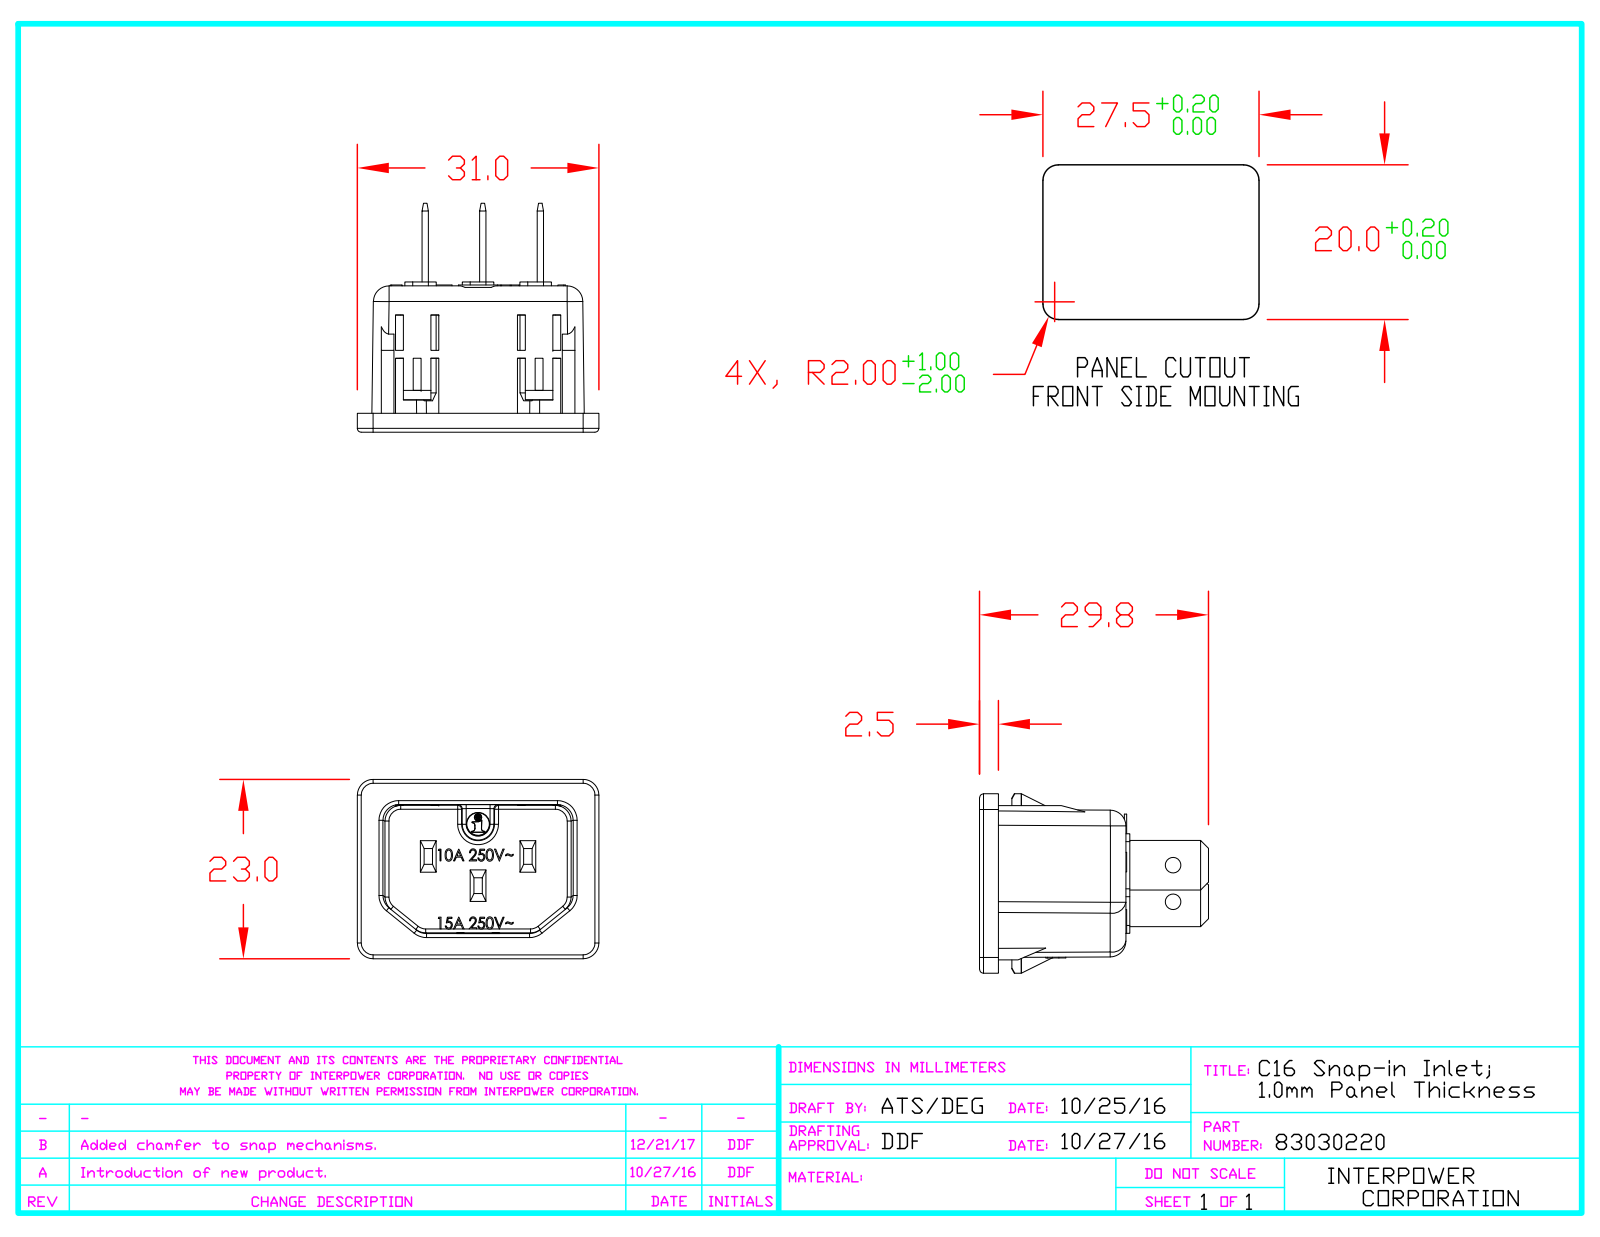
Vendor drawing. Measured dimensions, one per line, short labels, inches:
name: C16_Snap-in_BODY_1.0mm_R5_12-14-17; 55030530_R3_Contact_QD_GND_1-18-16; Contacts_Measured_L-N_QD.1; Contacts_C14-C16_QD_Assy (+2 more)
written by: PTC Creo Elements/Direct Modeling 19.0D 23-Nov-2015 (C) Parametric Technology GmbH (AUTOMOTIVE_DESIGN)
unit: in
bodies: 5 solids, 1780 faces (1614 planar, 119 cylindrical, 47 other)
size: 1.22 × 1.174 × 0.908
volume: 0.241 in³; area: 8.754 in²
holes: 2× ⌀0.069
rounds: 13× R0.039, 12× R0.02, 6× R0.049, 6× R0.079, 4× R0.015, 4× R0.02, 4× R0.023, 4× R0.023
face distances: 0.276, 0.551, 0.098, 0.65, 0.091, 0.74, 0.642, 0.032, 0.079, 0.047
hole spacings: 0.157
